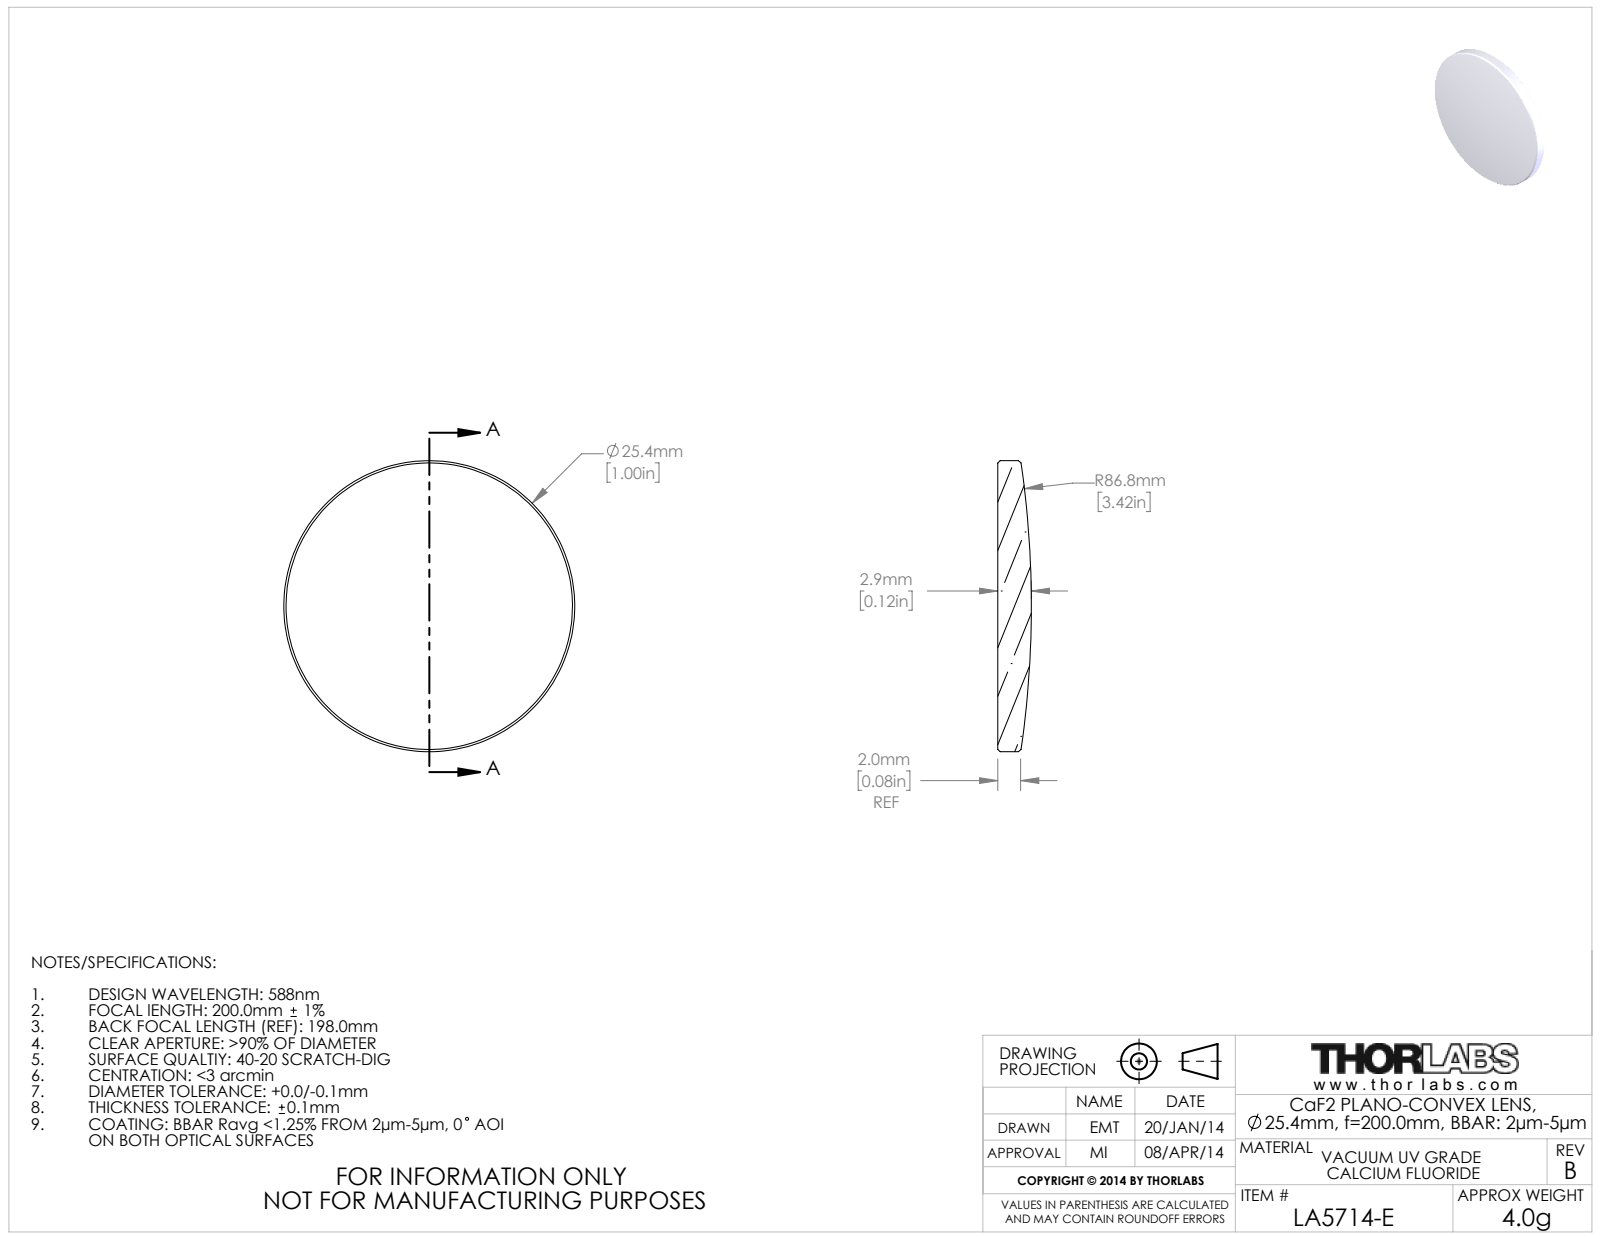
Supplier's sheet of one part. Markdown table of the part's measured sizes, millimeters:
| quantity | value |
| --- | --- |
| part name | 20136-E0W |
| STEP written by | SolidWorks 2018 (CONFIG_CONTROL_DESIGN) |
| units | millimeters |
| bodies | 1 solid, 9 faces (1 planar, 2 cylindrical, 6 other) |
| overall size | 25.4 × 25.4 × 2.93 |
| volume | 1 245 mm³ |
| surface area | 1 158 mm² |
| round bosses / shafts (diameter × count) | 25.4 × 1 |
